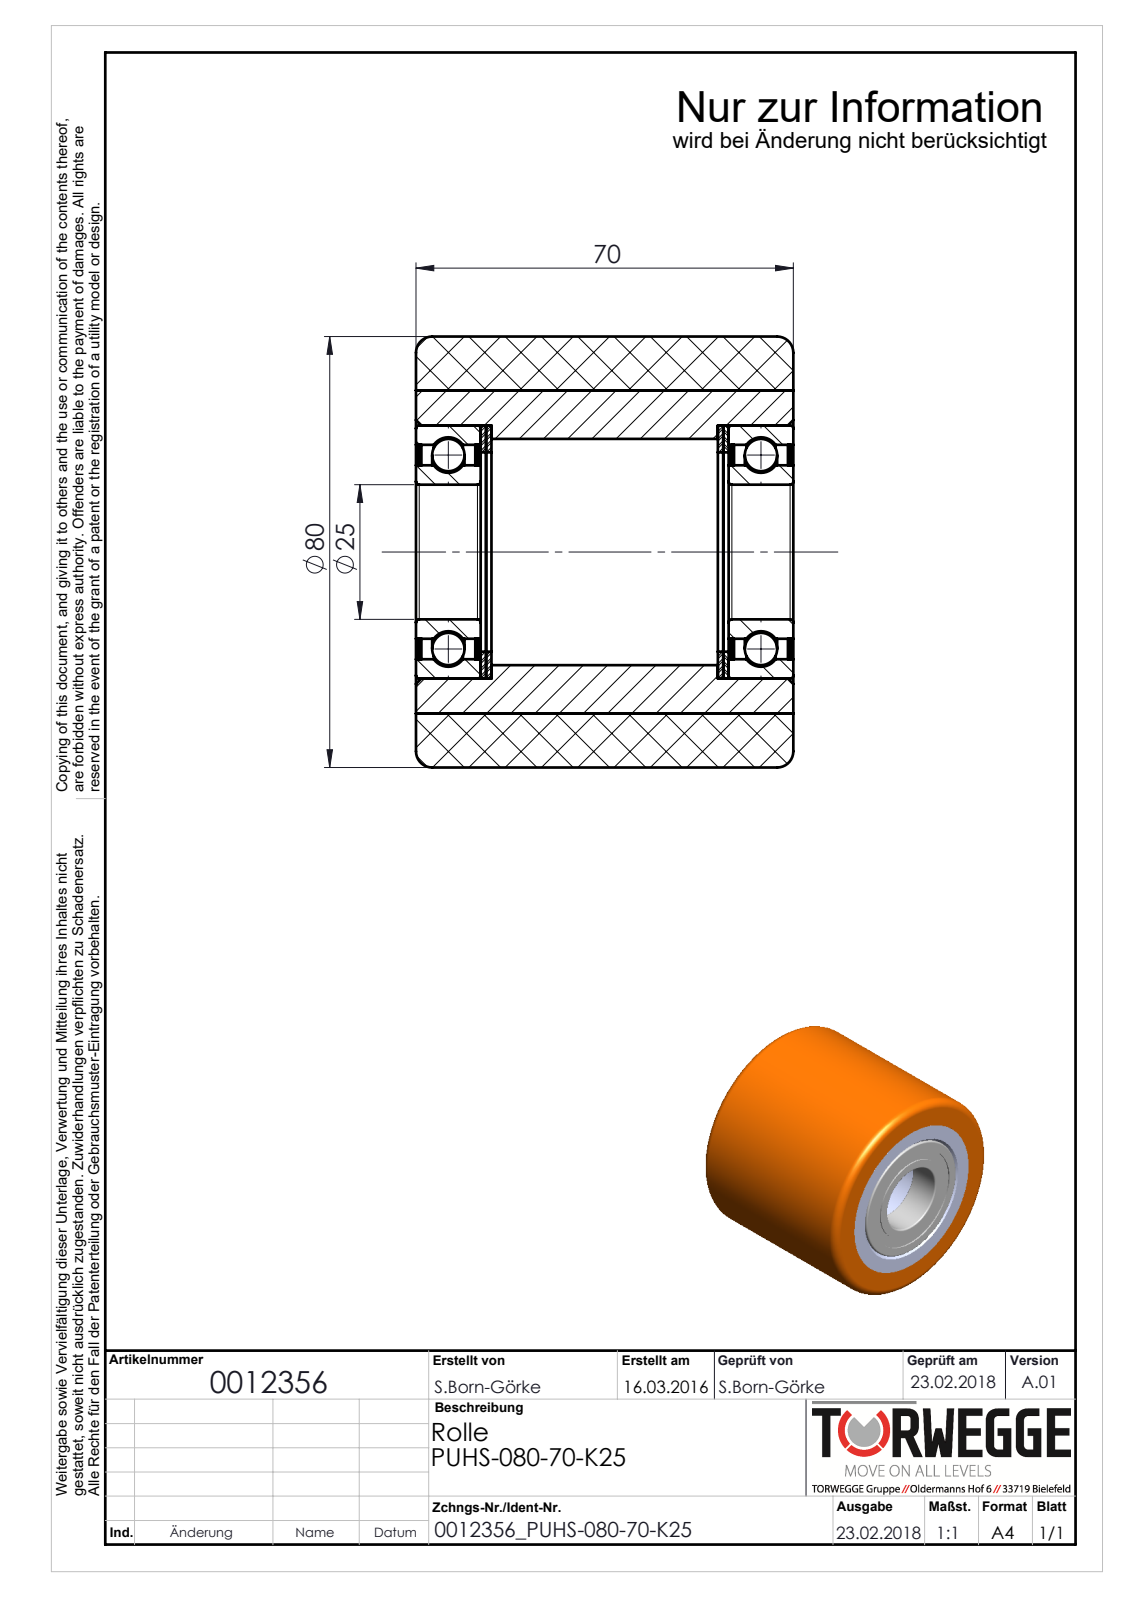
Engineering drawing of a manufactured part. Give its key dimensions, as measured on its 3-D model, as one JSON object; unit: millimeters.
{"part_name": "0012356_PUHS-080-70-K25", "step_written_by": "SolidWorks 2016 (AUTOMOTIVE_DESIGN)", "units": "millimeters", "bodies": {"solids": 16, "faces": 158, "planar": 30, "cylindrical": 68, "other": 60}, "overall_size": [80, 80, 70], "volume_mm3": 271475, "surface_area_mm2": 88685, "round_holes": [[25, 1], [32.2, 1], [37, 1], [39.8, 1], [42, 1], [60, 1]], "round_bosses_or_shafts": [[80, 1], [47, 1]], "face_to_face_distances": [1, 58, 12, 0.5, 13, 57, 45, 44, 70, 56]}
